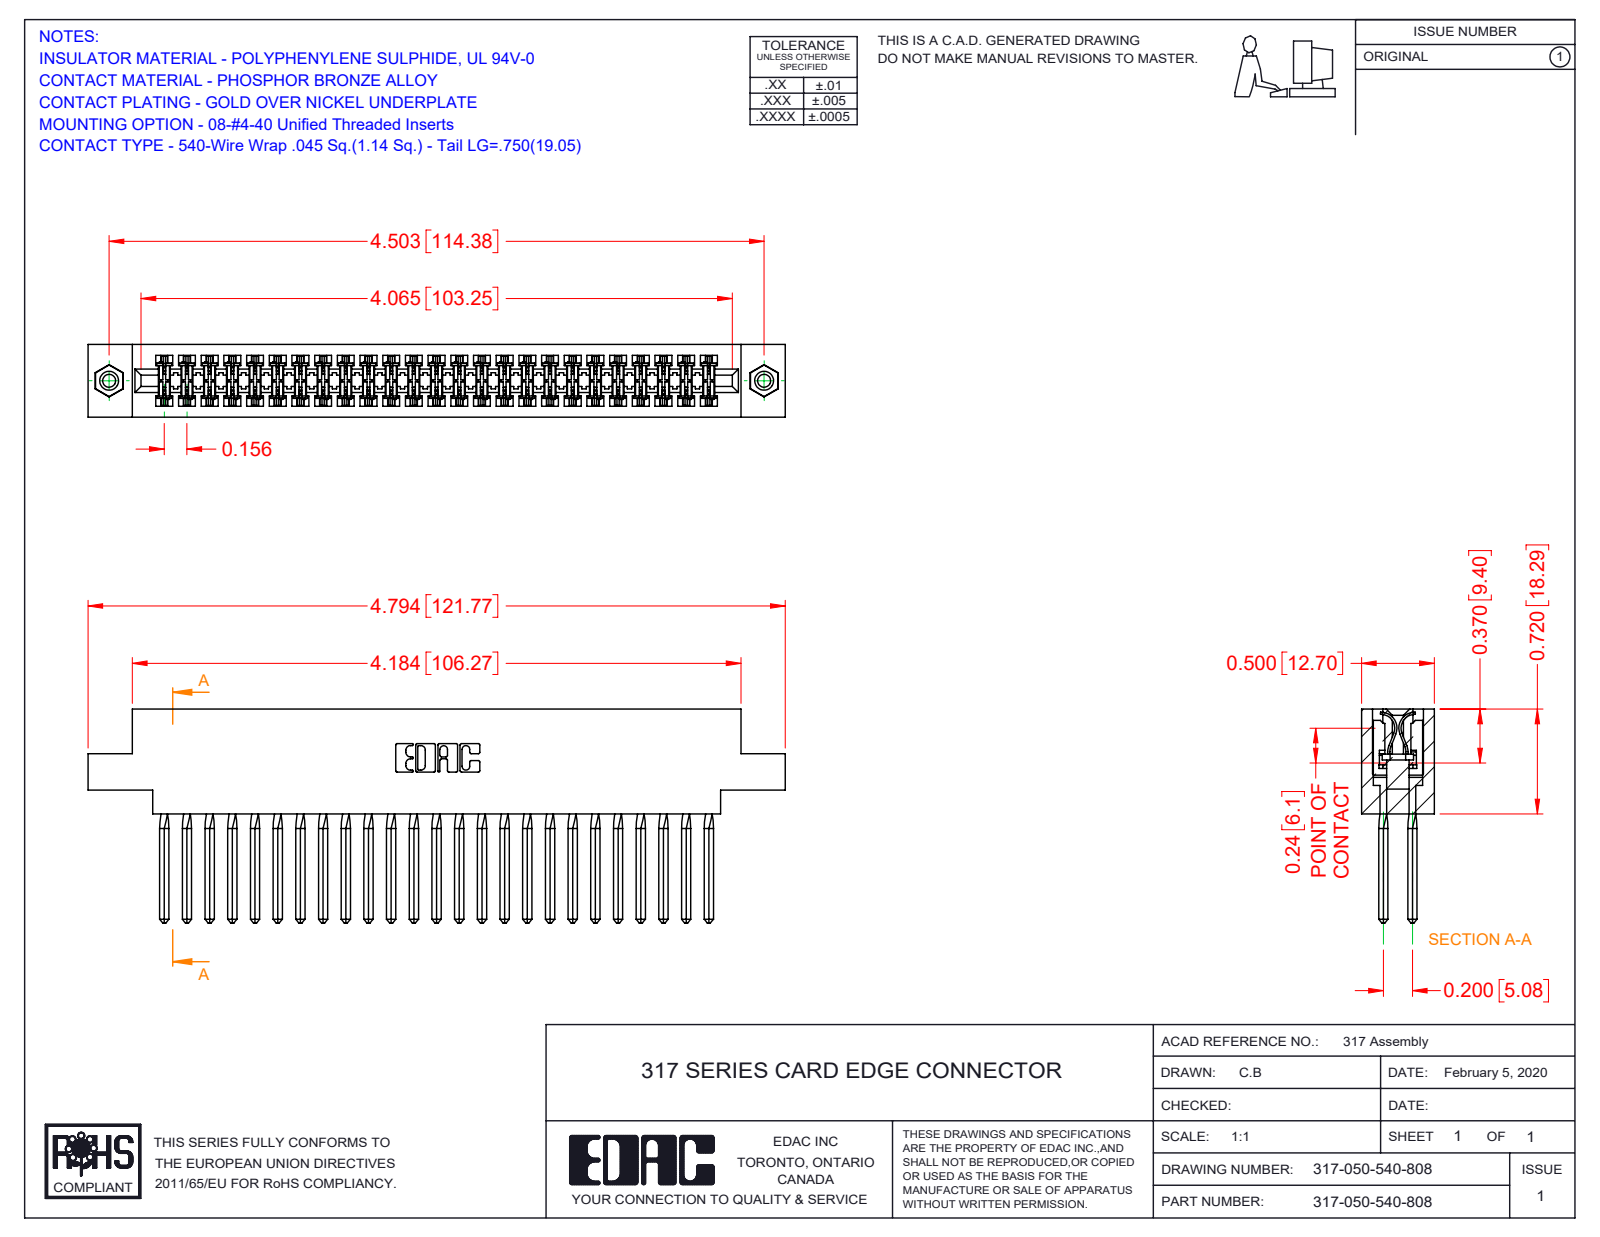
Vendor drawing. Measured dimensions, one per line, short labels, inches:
name: 317 Part_.156 Dia - TI; 345-250-001_345-250-003-102; 317-050-540-808; 317-290-001_540
written by: SolidWorks 2016 (CONFIG_CONTROL_DESIGN)
unit: in
bodies: 53 solids, 4612 faces (3740 planar, 656 cylindrical, 216 other)
size: 4.794 × 1.47 × 0.5
volume: 1.212 in³; area: 44.92 in²
holes: 2× ⌀0.089, 2× ⌀0.125, 2× ⌀0.156
bosses: 2× ⌀0.155
rounds: 100× R0.015, 22× R0.01, 6× R0.007, 6× R0.031, 3× R0.026, 2× R0.095, 2× R0.1, 2× R0.11
face distances: 0.5, 0.075, 0.425, 0.35, 0.11, 0.195, 0.094, 0.72, 0.2, 0.115
hole spacings: 4.503
